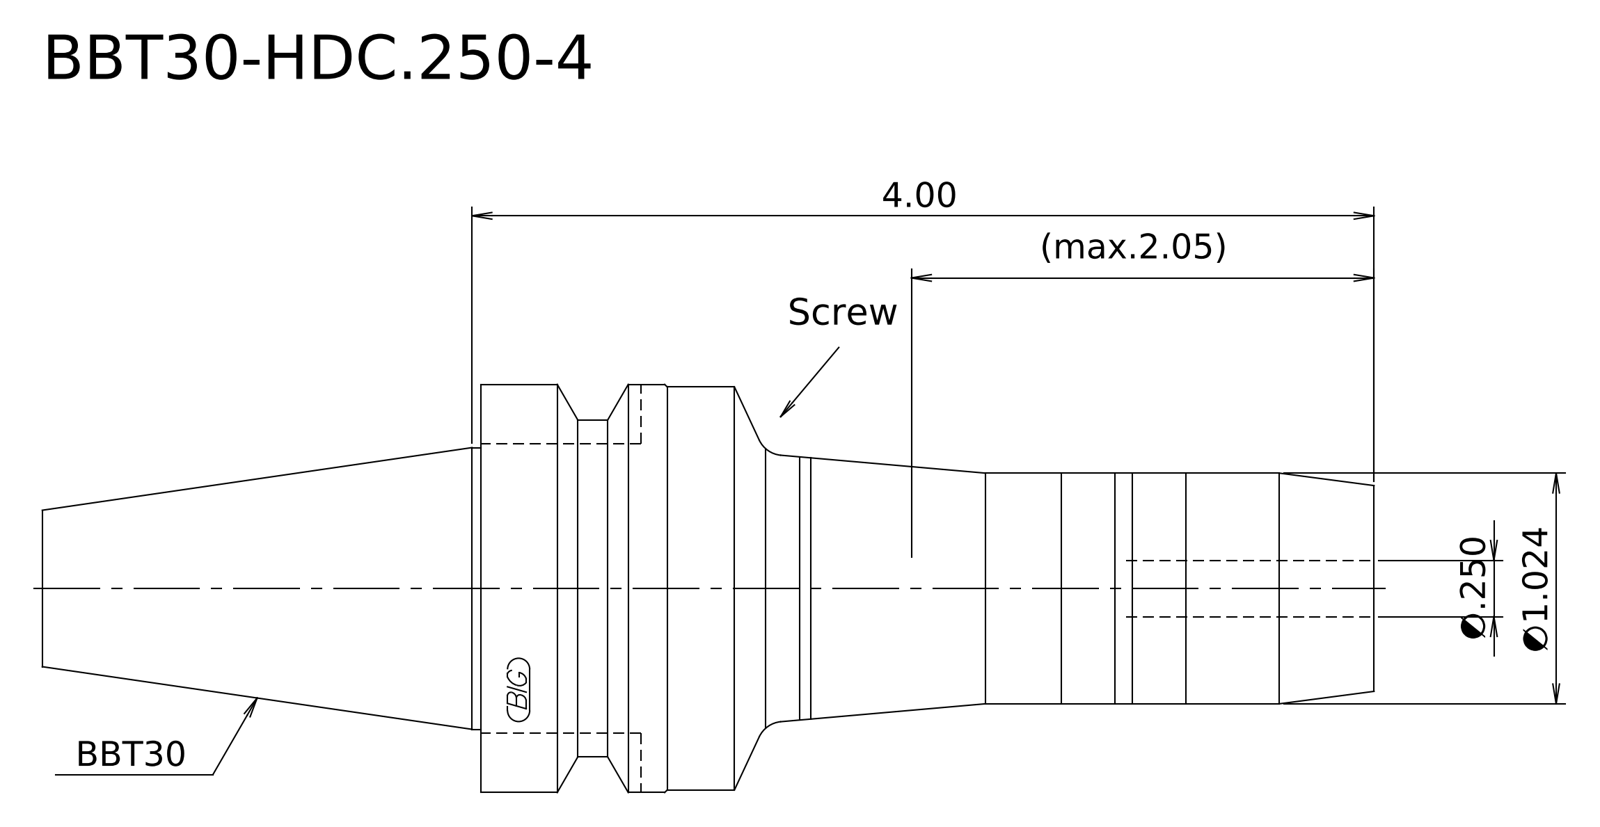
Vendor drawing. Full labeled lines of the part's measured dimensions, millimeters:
STEP written by: Kubotek KeyCreator 2011 V10.0.2 (22737) (automotive_design)
Units: millimetres
Bodies: 1 solid, 16 faces (3 planar, 6 cylindrical, 7 other)
Overall size (bounding box): 150 × 46 × 46
Volume: 111 495 mm³ · Surface area: 16 700 mm²
Round bosses / shafts (diameter × count): ⌀46 ×1, ⌀45.4 ×1, ⌀38 ×1, ⌀31.75 ×1, ⌀26 ×1
Main face-to-face distances: 100.6, 150, 49.4
